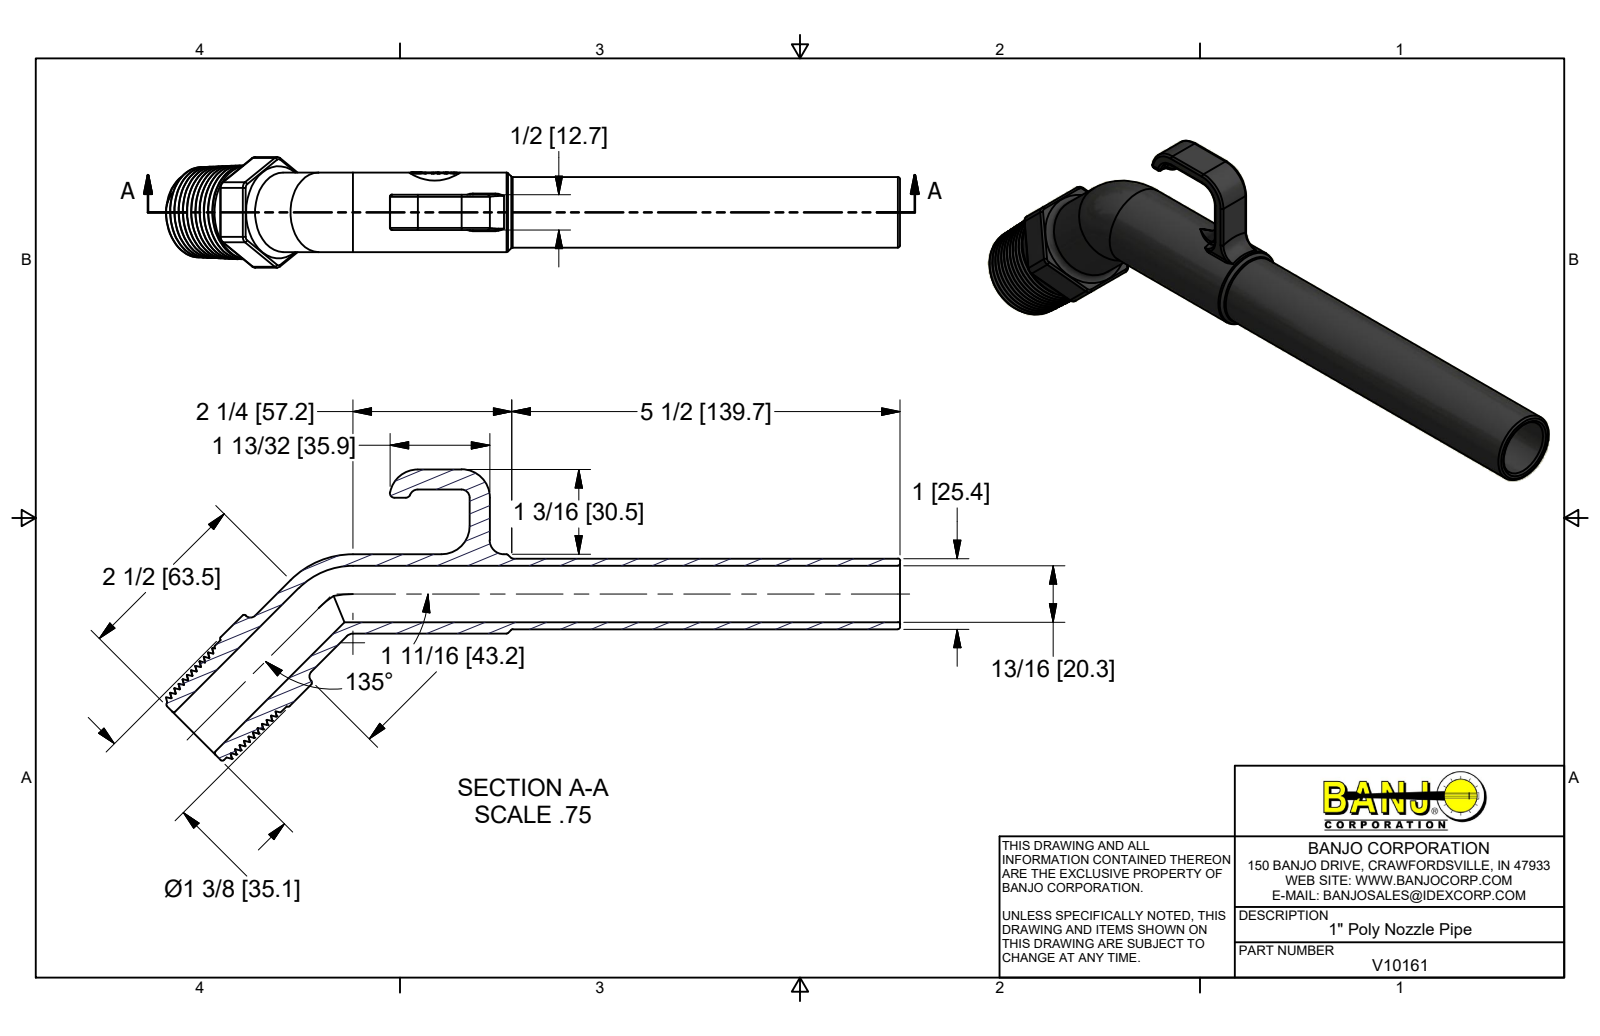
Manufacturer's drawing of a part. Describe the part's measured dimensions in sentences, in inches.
The part is named "V10161". Its 3-D file was written by "Autodesk Inventor 2017 (AUTOMOTIVE_DESIGN)". It is 1 solid with 408 faces: 117 planar, 82 cylindrical and 209 other. Overall it measures 10.401 by 4.124 by 1.566 inches. Its volume is 4.999 cubic inches and its surface area 72.18 square inches. Round holes: 2 of diameter 0.8. Round bosses or shafts: 2 of diameter 1.125, 1 of diameter 1.325, 1 of diameter 1. Partial cylindrical surfaces (rounded edges, fillets, slot ends): 28 of radius 0.03, 6 of radius 0.09, 4 of radius 0.065, 2 of radius 0.125, 2 of radius 0.24, 2 of radius 0.4, 1 of radius 0.352, 1 of radius 0.552. The main face-to-face distances are 1.38, 1.38, 1.381, 0.5, 1.7, 1.2, 0.5, 5.813, 0.16, 0.16.
